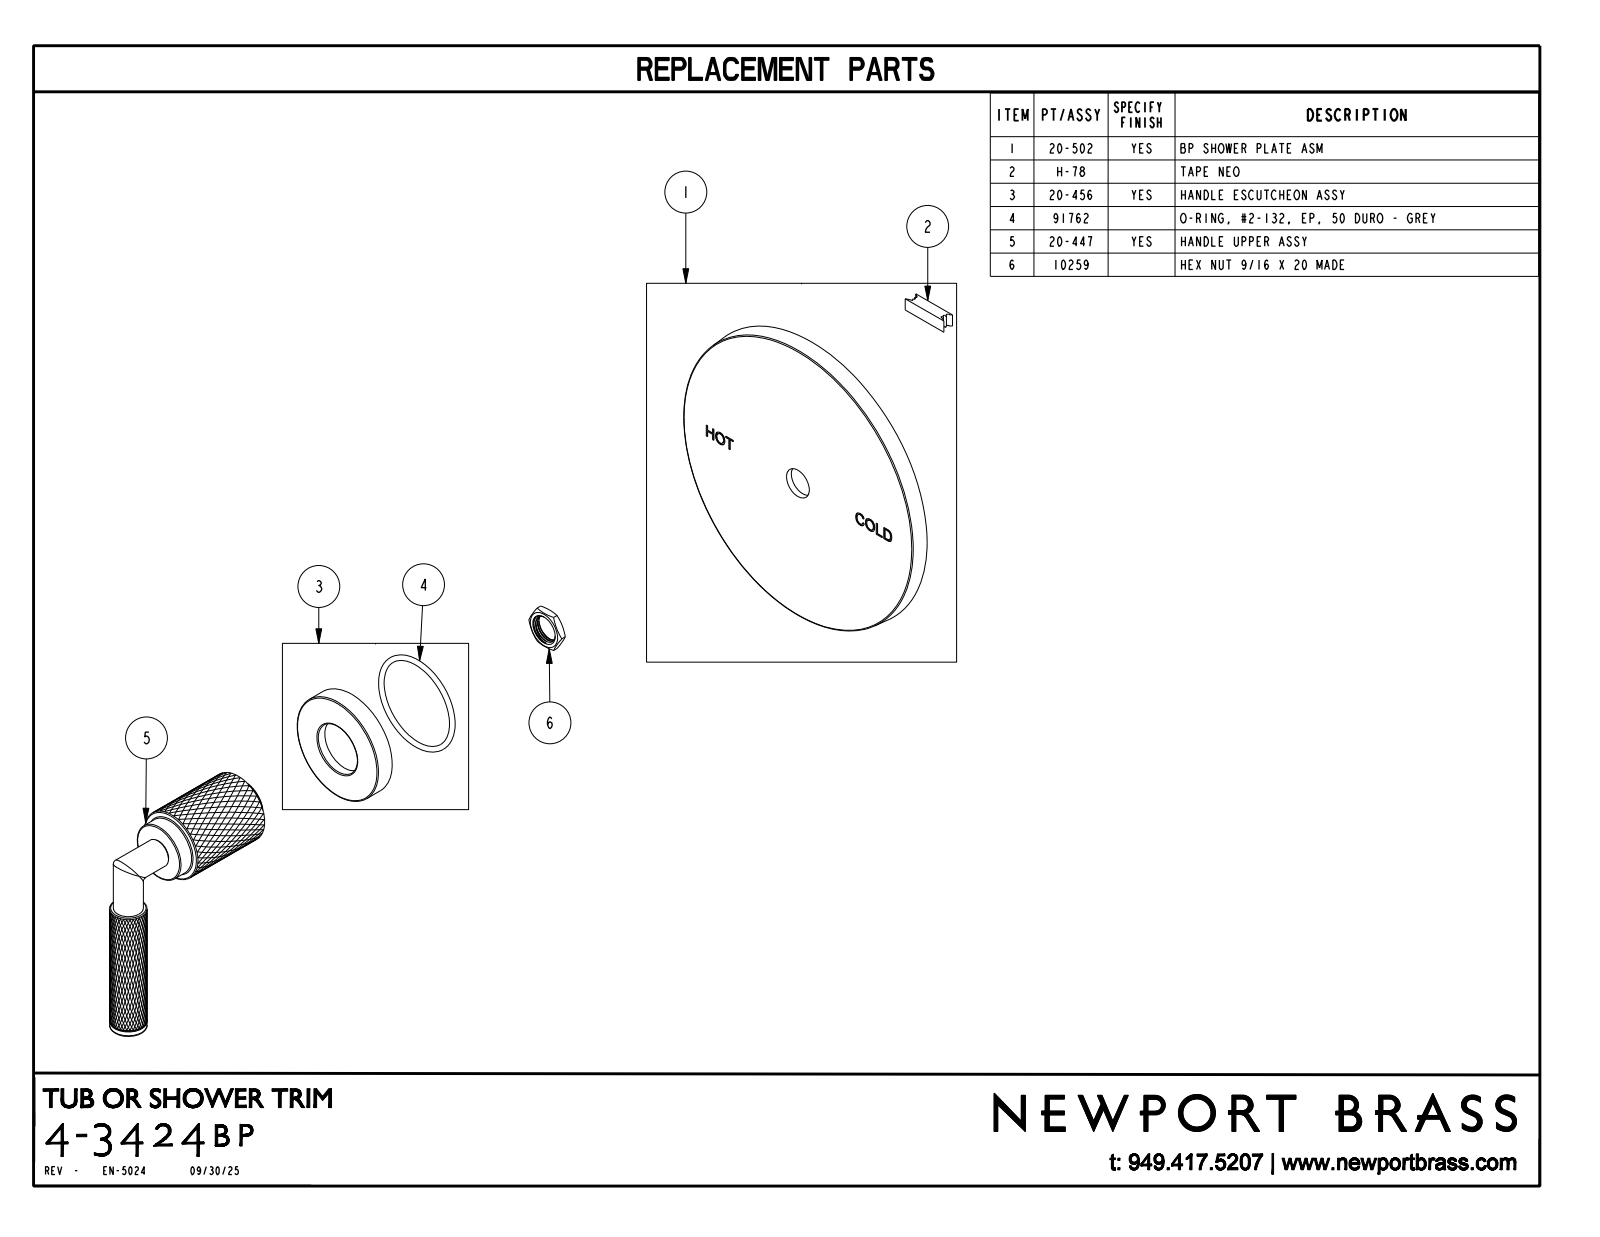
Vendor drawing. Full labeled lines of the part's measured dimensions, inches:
Part name (STEP PRODUCT): 4-3424BP
STEP written by: CREO PARAMETRIC BY PTC INC, 2025093 (CONFIG_CONTROL_DESIGN)
Units: inches
Bodies: 1 solid, 18987 faces (53 planar, 3698 cylindrical, 15236 other)
Overall size (bounding box): 6.505 × 6 × 3.915
Volume: 15.34 in³ · Surface area: 85.25 in²
Round bosses / shafts (diameter × count): ⌀0.55 ×2, ⌀2.1 ×1, ⌀1.375 ×1, ⌀1.125 ×1, ⌀0.688 ×1, ⌀0.687 ×1, ⌀0.5 ×1
Main face-to-face distances: 0.35, 0.725, 0.375, 2.787, 2.437, 2.063, 2.476, 2.126, 1.751, 0.312
